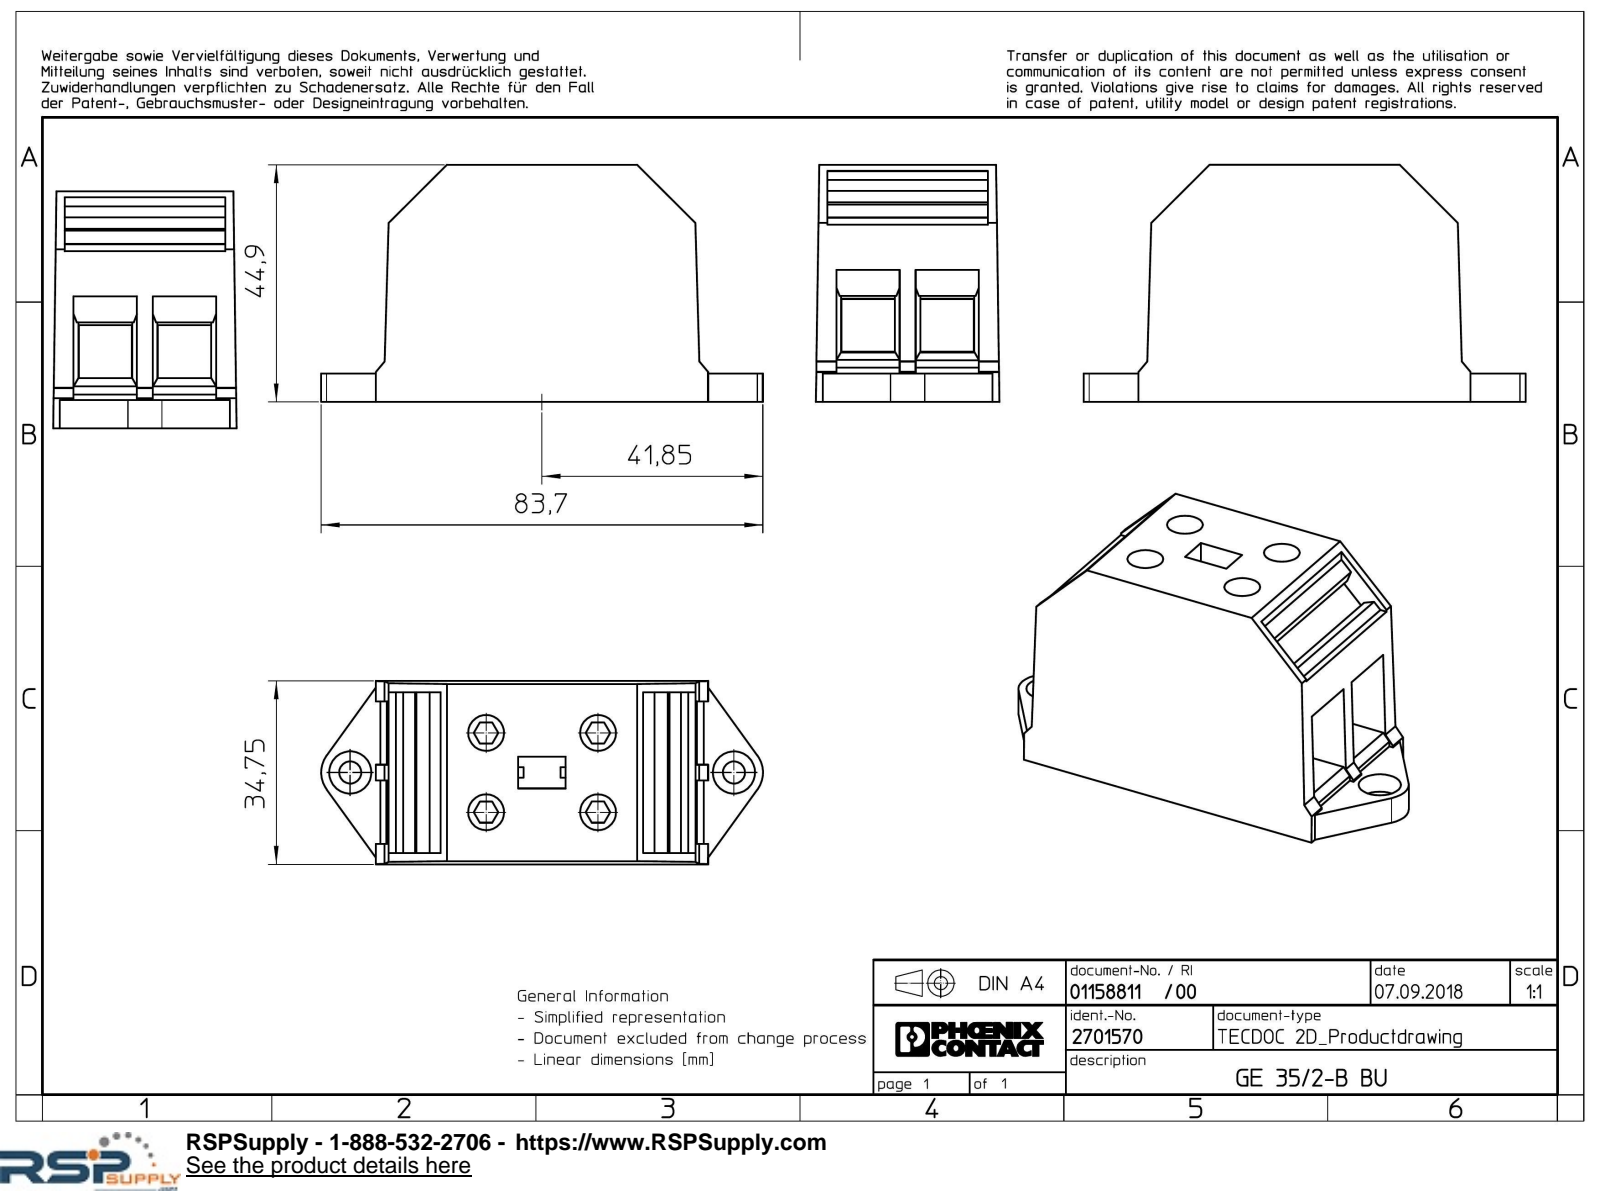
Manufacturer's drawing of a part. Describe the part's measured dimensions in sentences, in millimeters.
The part is named "GE_35_2-B_BU-SELECT". Its 3-D file was written by "Creo Elements/Direct Modeling 20.1A 29-Sep-2018 (C) Parametric Technology GmbH (AUTOMOTIVE_DESIGN)". It is 1 solid with 197 faces: 177 planar, 20 cylindrical and 0 other. Overall it measures 83.7 by 45.37 by 34.75 millimeters. Its volume is 70 054 cubic millimeters and its surface area 19 153 square millimeters. Round holes: 4 of diameter 6.8, 2 of diameter 4.2, 2 of diameter 8. Partial cylindrical surfaces (rounded edges, fillets, slot ends): 2 of radius 1, 2 of radius 5.5. The main face-to-face distances are 15, 0.95, 11.05, 44.9, 9.55, 12, 26.05, 10.1, 25.4, 19.5. The hole center spacings are 26.82, 47.55, 15, 21.2, 25.97, 72.7.
